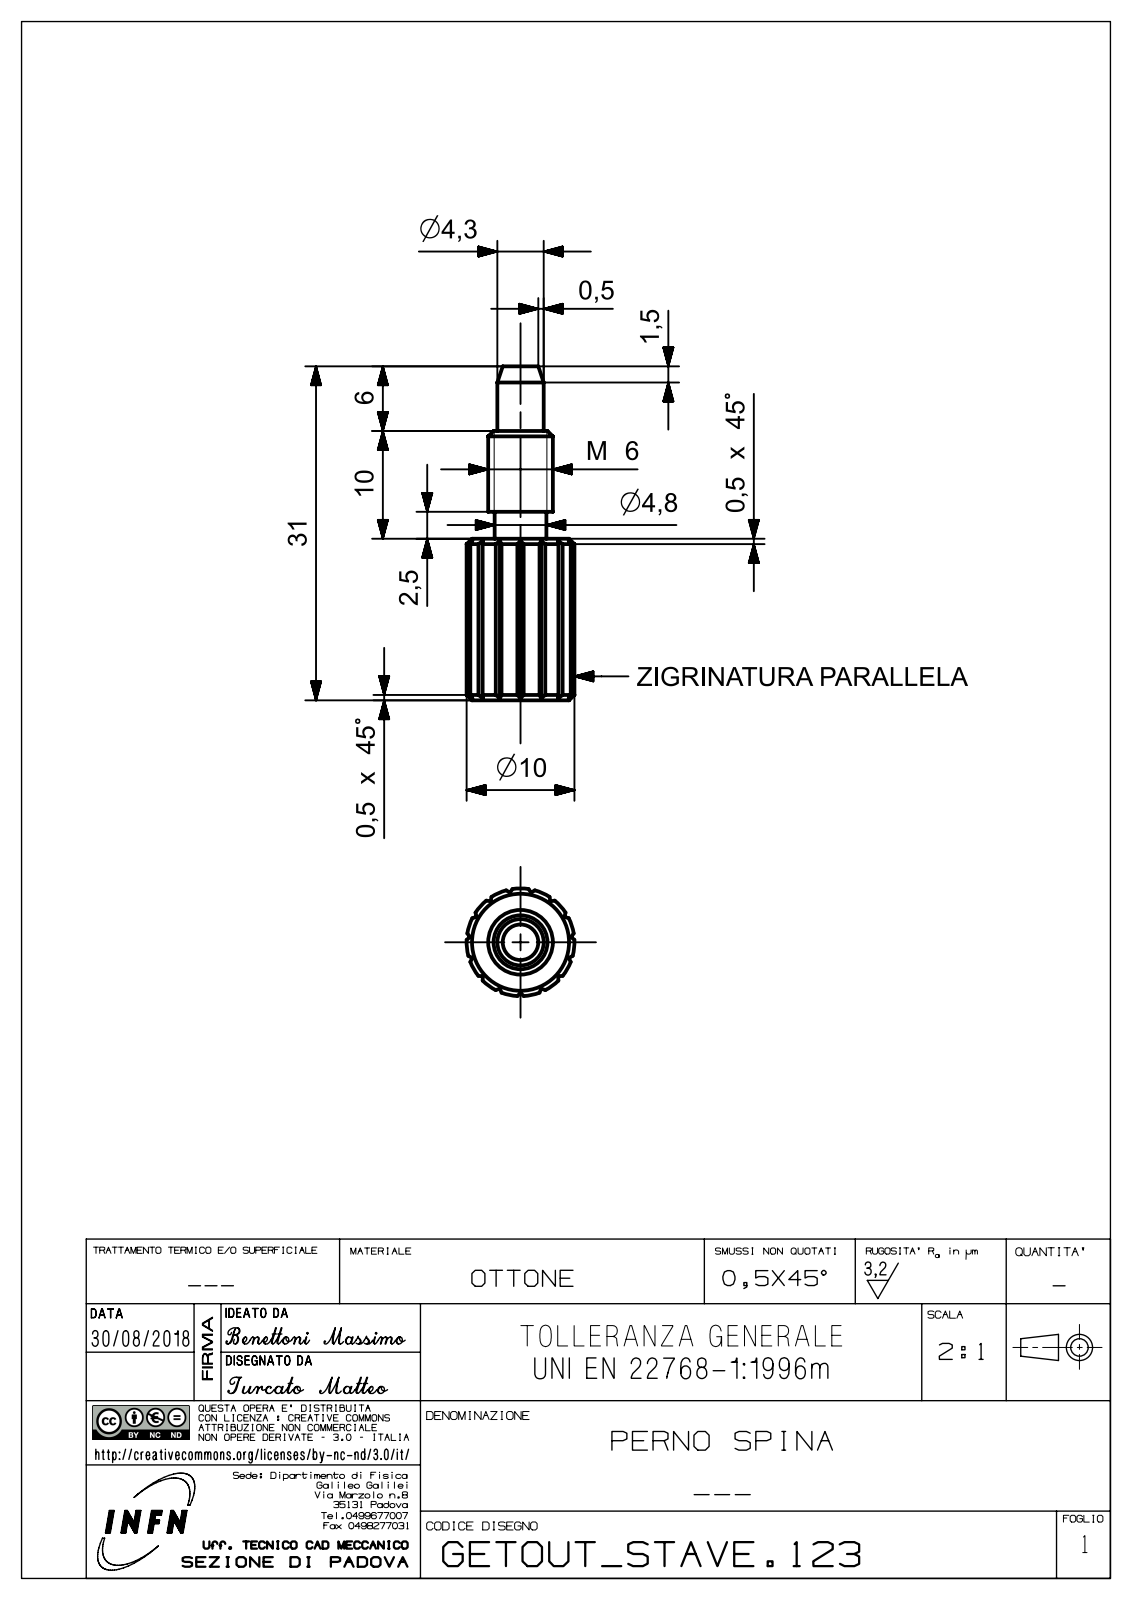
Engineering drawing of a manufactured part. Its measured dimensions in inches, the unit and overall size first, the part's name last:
Units: inches
Overall size (bounding box): 1.22 × 0.394 × 0.393
Round bosses / shafts (diameter × count): ⌀0.236 ×1, ⌀0.189 ×1, ⌀0.169 ×1
Partial cylindrical surfaces — rounded edges, fillets, slot ends (radius × count): R0.197 ×1
Main face-to-face distances: 0.591, 0.689, 0.098, 1.22, 0.63, 0.531, 0.984, 0.394, 0.295, 0.236
Volume: 0.091 in³ · Surface area: 1.44 in²
Bodies: 1 solid, 57 faces (35 planar, 18 cylindrical, 4 other)
Part name (STEP PRODUCT): bezA730AE56cd2s
STEP written by: SIEMENS PLM Software NX 12.0 (AUTOMOTIVE_DESIGN)
